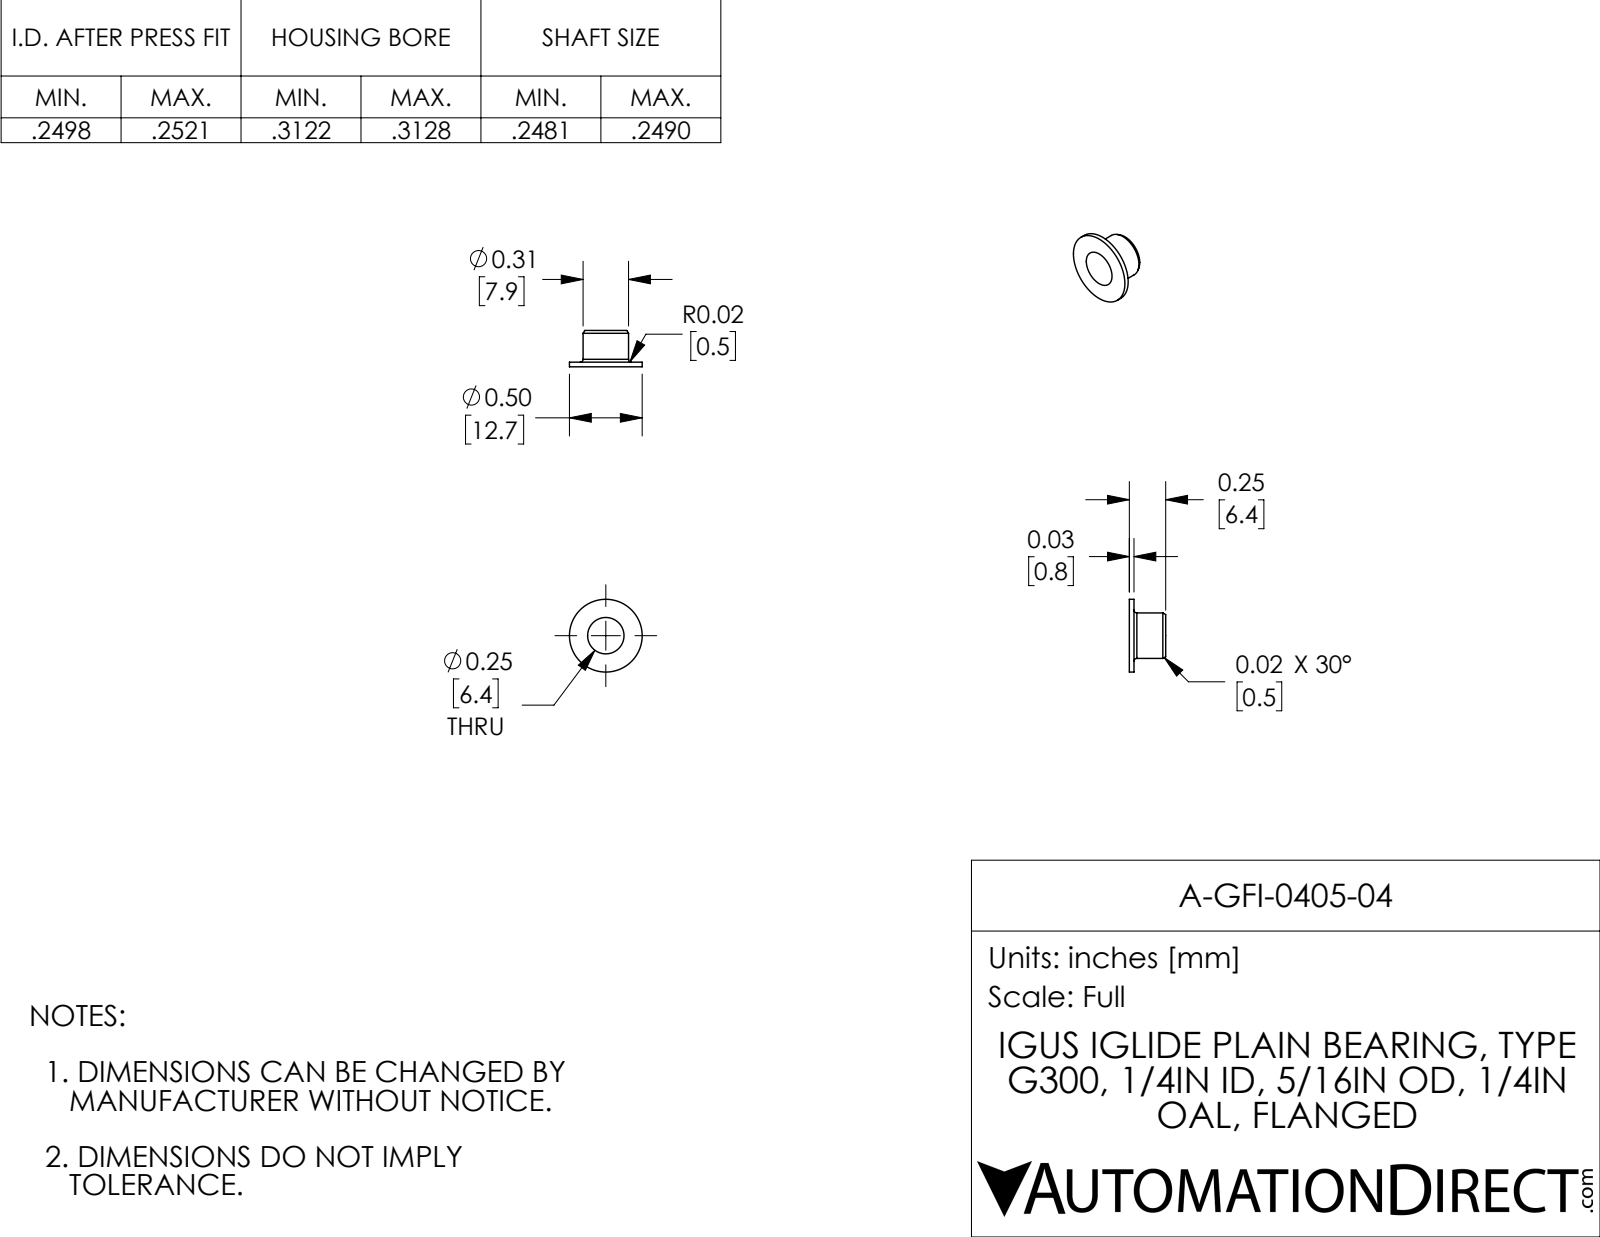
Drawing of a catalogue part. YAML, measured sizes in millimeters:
part_name: "A-GFI-0405-04"
step_written_by: "SolidWorks 2017 (AUTOMOTIVE_DESIGN)"
units: millimeters
bodies: {solids: 1, faces: 13, planar: 3, cylindrical: 6, other: 4}
overall_size: [12.7, 12.7, 6.4]
volume: 180
surface_area: 476
round_holes:
  - {diameter: 6.4, count: 1}
round_bosses_or_shafts:
  - {diameter: 12.7, count: 1}
  - {diameter: 8, count: 1}
face_to_face_distances: [0.8, 6.4, 5.5]
